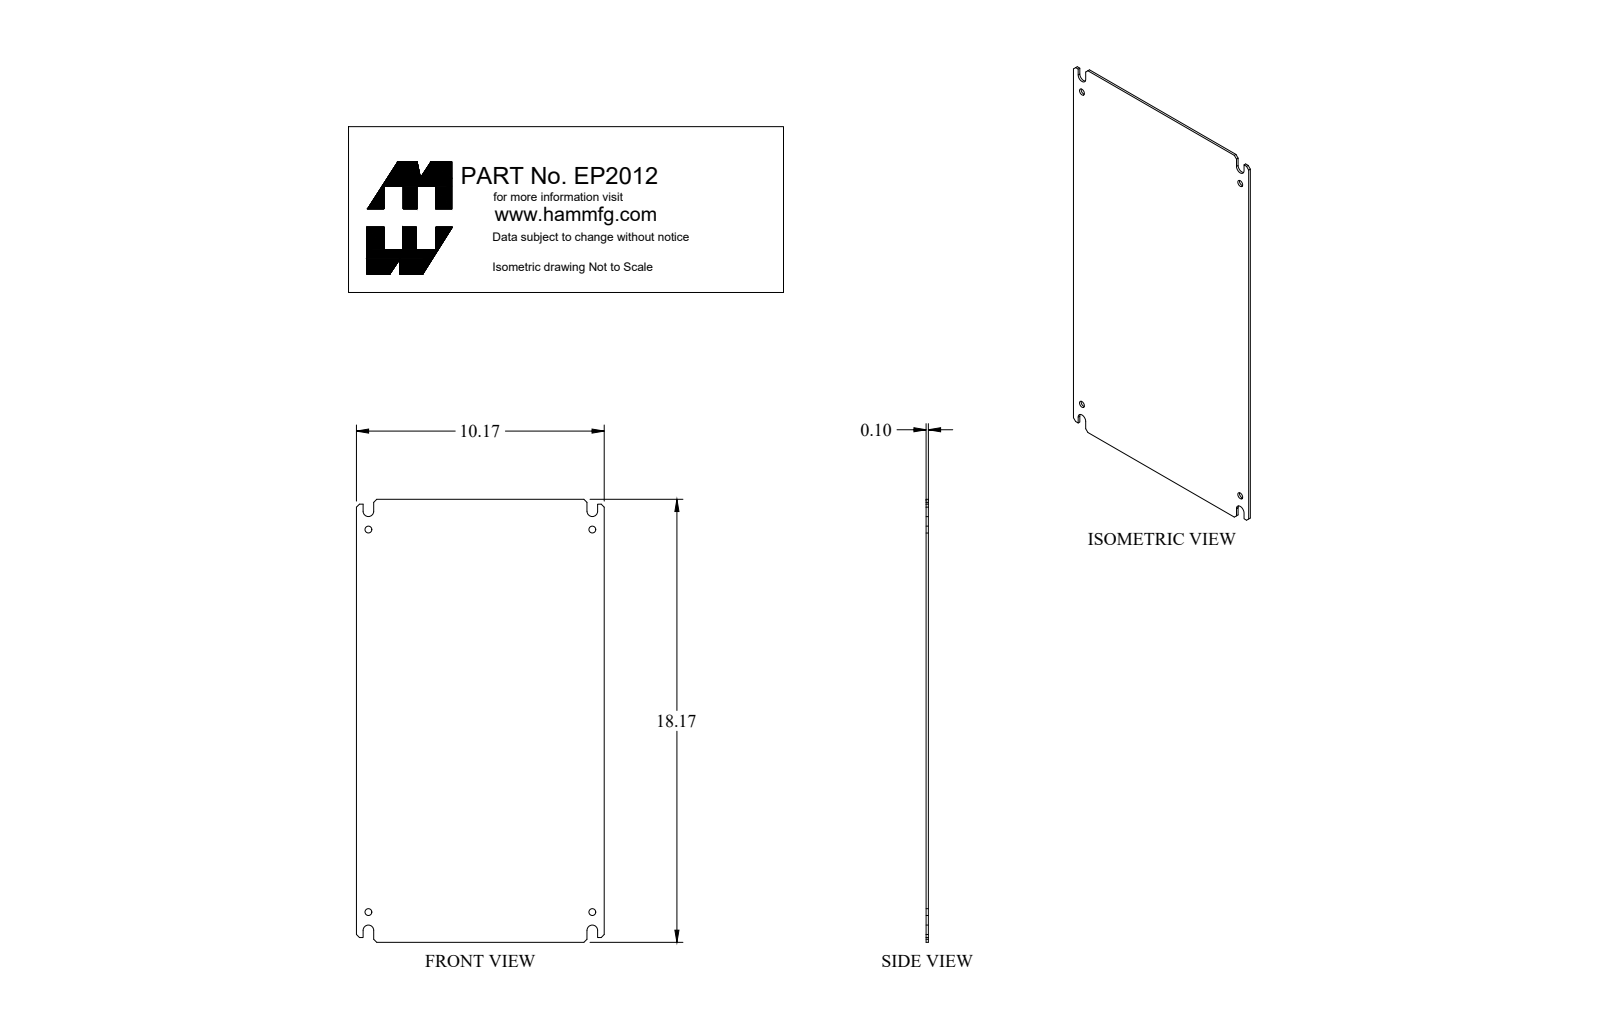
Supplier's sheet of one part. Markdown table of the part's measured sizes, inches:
| quantity | value |
| --- | --- |
| part name | EP2012 |
| STEP written by | SolidWorks 2018 (AUTOMOTIVE_DESIGN) |
| units | inches |
| bodies | 1 solid, 40 faces (26 planar, 14 cylindrical, 0 other) |
| overall size | 18.17 × 10.17 × 0.095 |
| volume | 17.4 in³ |
| surface area | 372.2 in² |
| round holes (diameter × count) | 0.281 × 4 |
| partial cylindrical surfaces (radius × count) | 0.219 × 4 |
| main face-to-face distances | 0.095, 10.17, 18.17, 0.709, 9.461, 0.272, 9.898, 0.437, 9.188, 8.751 |
| hole center spacings | 9.188, 15.688, 18.181 |
